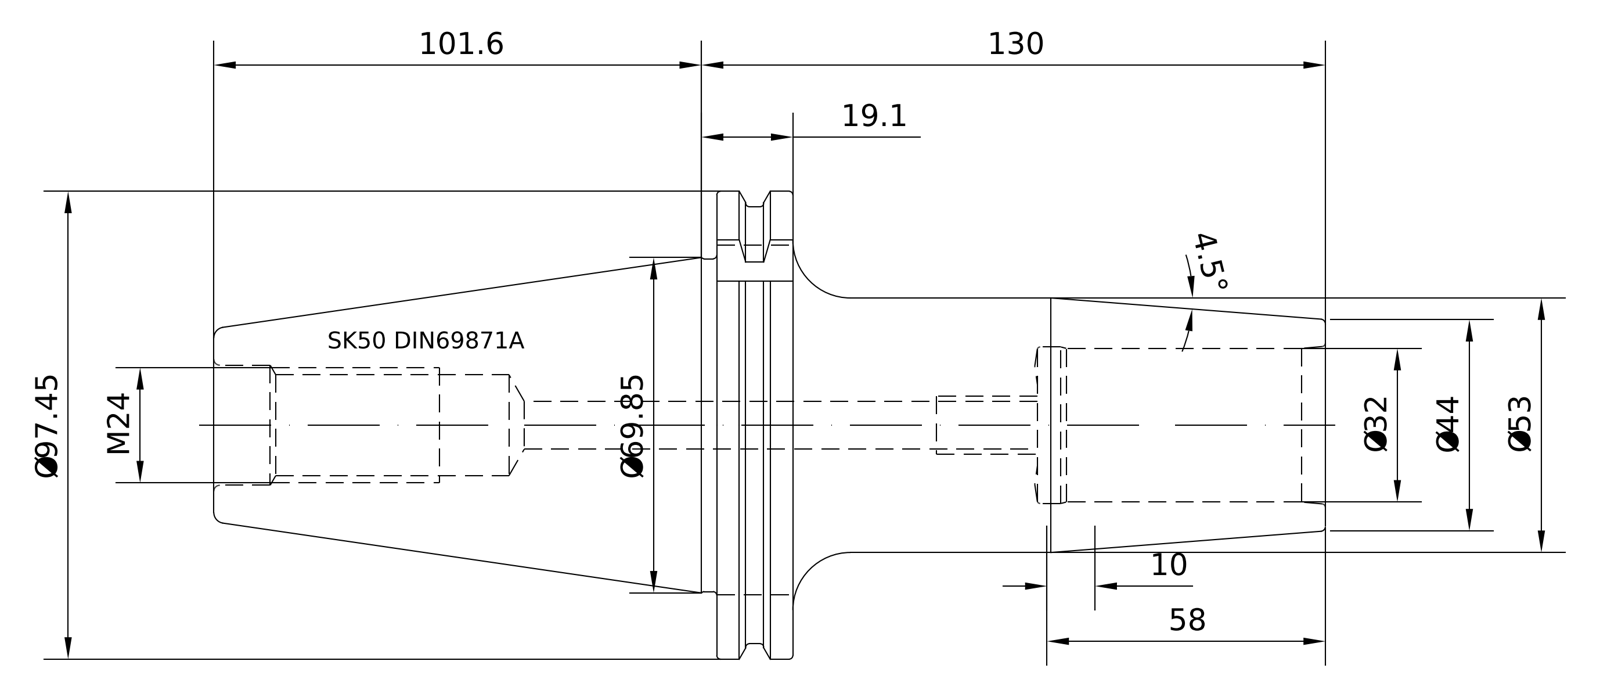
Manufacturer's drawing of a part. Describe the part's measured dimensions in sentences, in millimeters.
The part is named "50-444-32". Its 3-D file was written by "PRO/ENGINEER BY PARAMETRIC TECHNOLOGY CORPORATION, 2010430 (CONFIG_CONTROL_DESIGN)". It is 1 solid with 94 faces: 22 planar, 24 cylindrical and 48 other. Overall it measures 231.6 by 97.47 by 94 millimeters. Its volume is 522 891 cubic millimeters and its surface area 64 643 square millimeters. Round holes: 1 of diameter 20.75, 1 of diameter 25.01, 1 of diameter 25.7, 1 of diameter 32. Round bosses or shafts: 1 of diameter 91, 1 of diameter 69.15, 1 of diameter 53, 1 of diameter 24.01. Partial cylindrical surfaces (rounded edges, fillets, slot ends): 1 of radius 1.75, 1 of radius 48.74. The main face-to-face distances are 15.85, 68.8, 52.95, 126.8, 110.95, 58, 72.8, 104.8, 120.65, 173.6.
